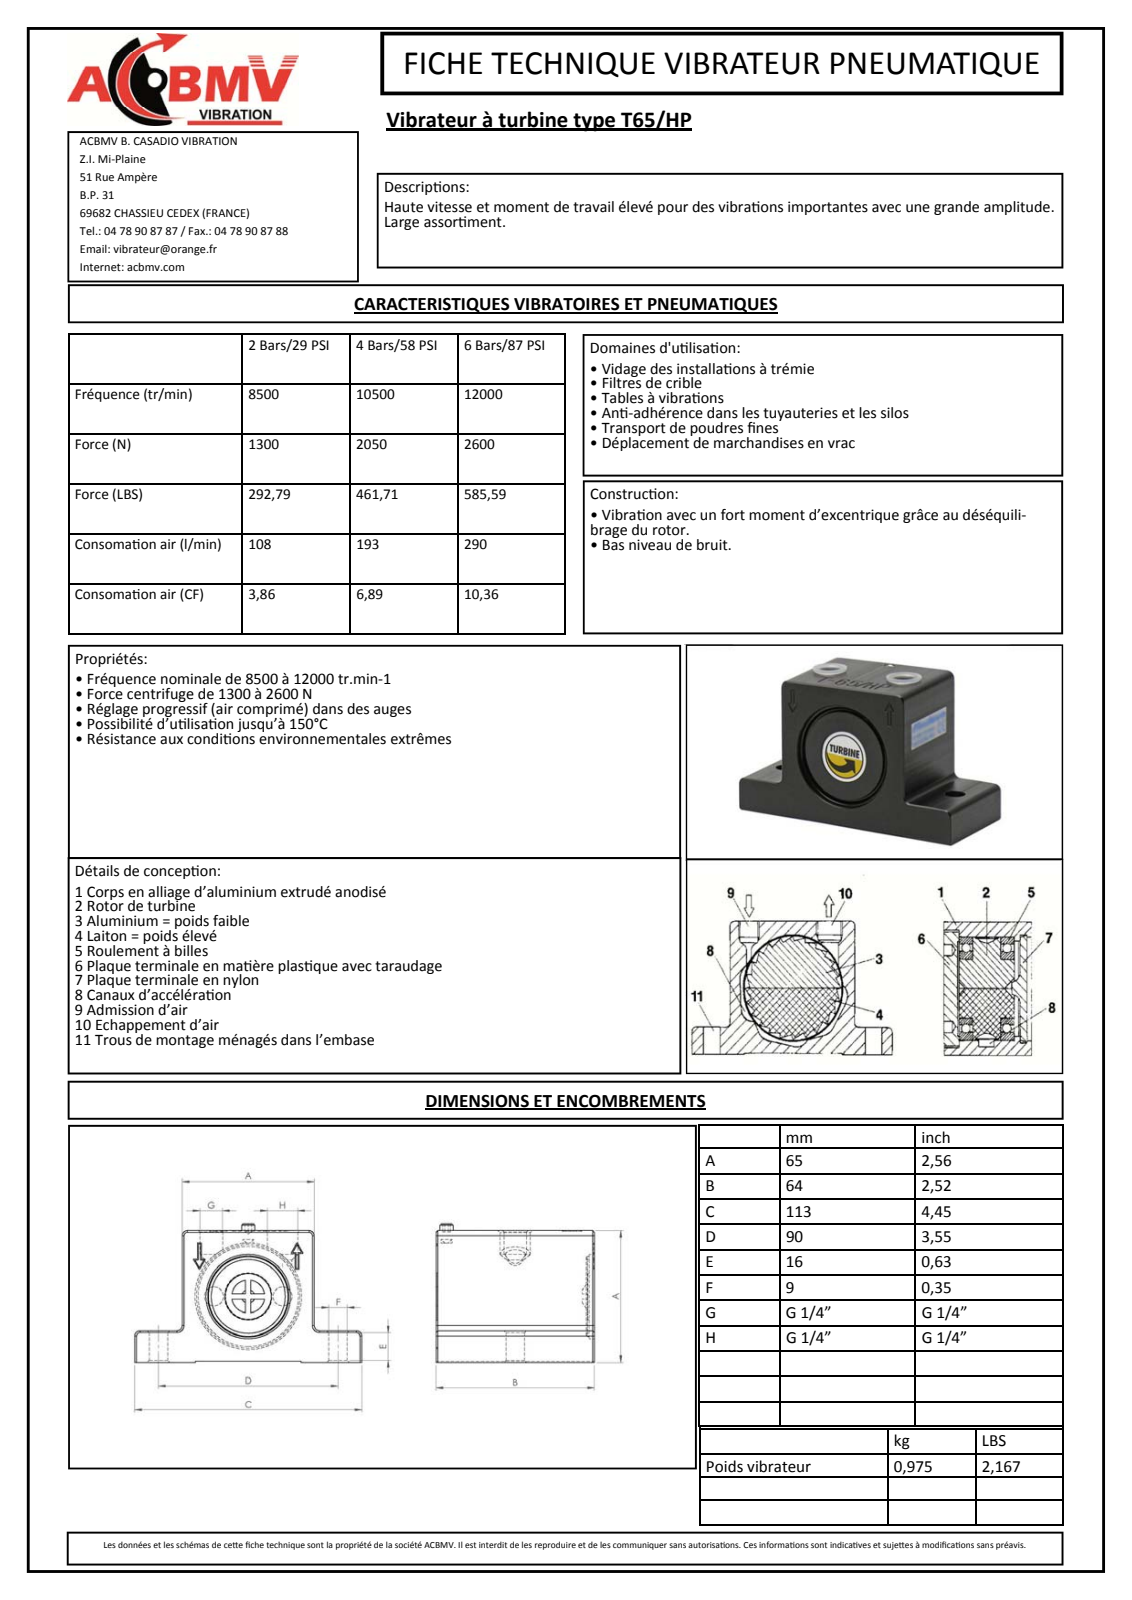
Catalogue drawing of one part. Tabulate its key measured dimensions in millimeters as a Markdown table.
| quantity | value |
| --- | --- |
| part name | 8065-20-M |
| STEP written by | Autodesk Inventor 2011 (CONFIG_CONTROL_DESIGN) |
| units | millimeters |
| bodies | 1 solid, 367 faces (228 planar, 98 cylindrical, 41 other) |
| overall size | 113 × 67.5 × 64 |
| volume | 308 011 mm³ |
| surface area | 34 750 mm² |
| round holes (diameter × count) | 7.2 × 2, 9 × 2, 11.45 × 2, 2.39 × 1, 4.13 × 1, 24.5 × 1, 25.4 × 1, 45.24 × 1, 47 × 1 |
| round bosses / shafts (diameter × count) | 41 × 1, 5 × 1, 2.15 × 1 |
| partial cylindrical surfaces (radius × count) | 0.25 × 18, 0.2 × 14, 2.5 × 6, 1.65 × 5, 2.15 × 5, 0.62 × 4, 0.41 × 3, 0.72 × 3 |
| main face-to-face distances | 65, 0.5, 64.5, 64, 16, 15.5, 49, 24, 89, 62 |
| hole center spacings | 20, 52.74, 17.38, 20.09, 24.5, 26.5, 32.65, 33.14 |
